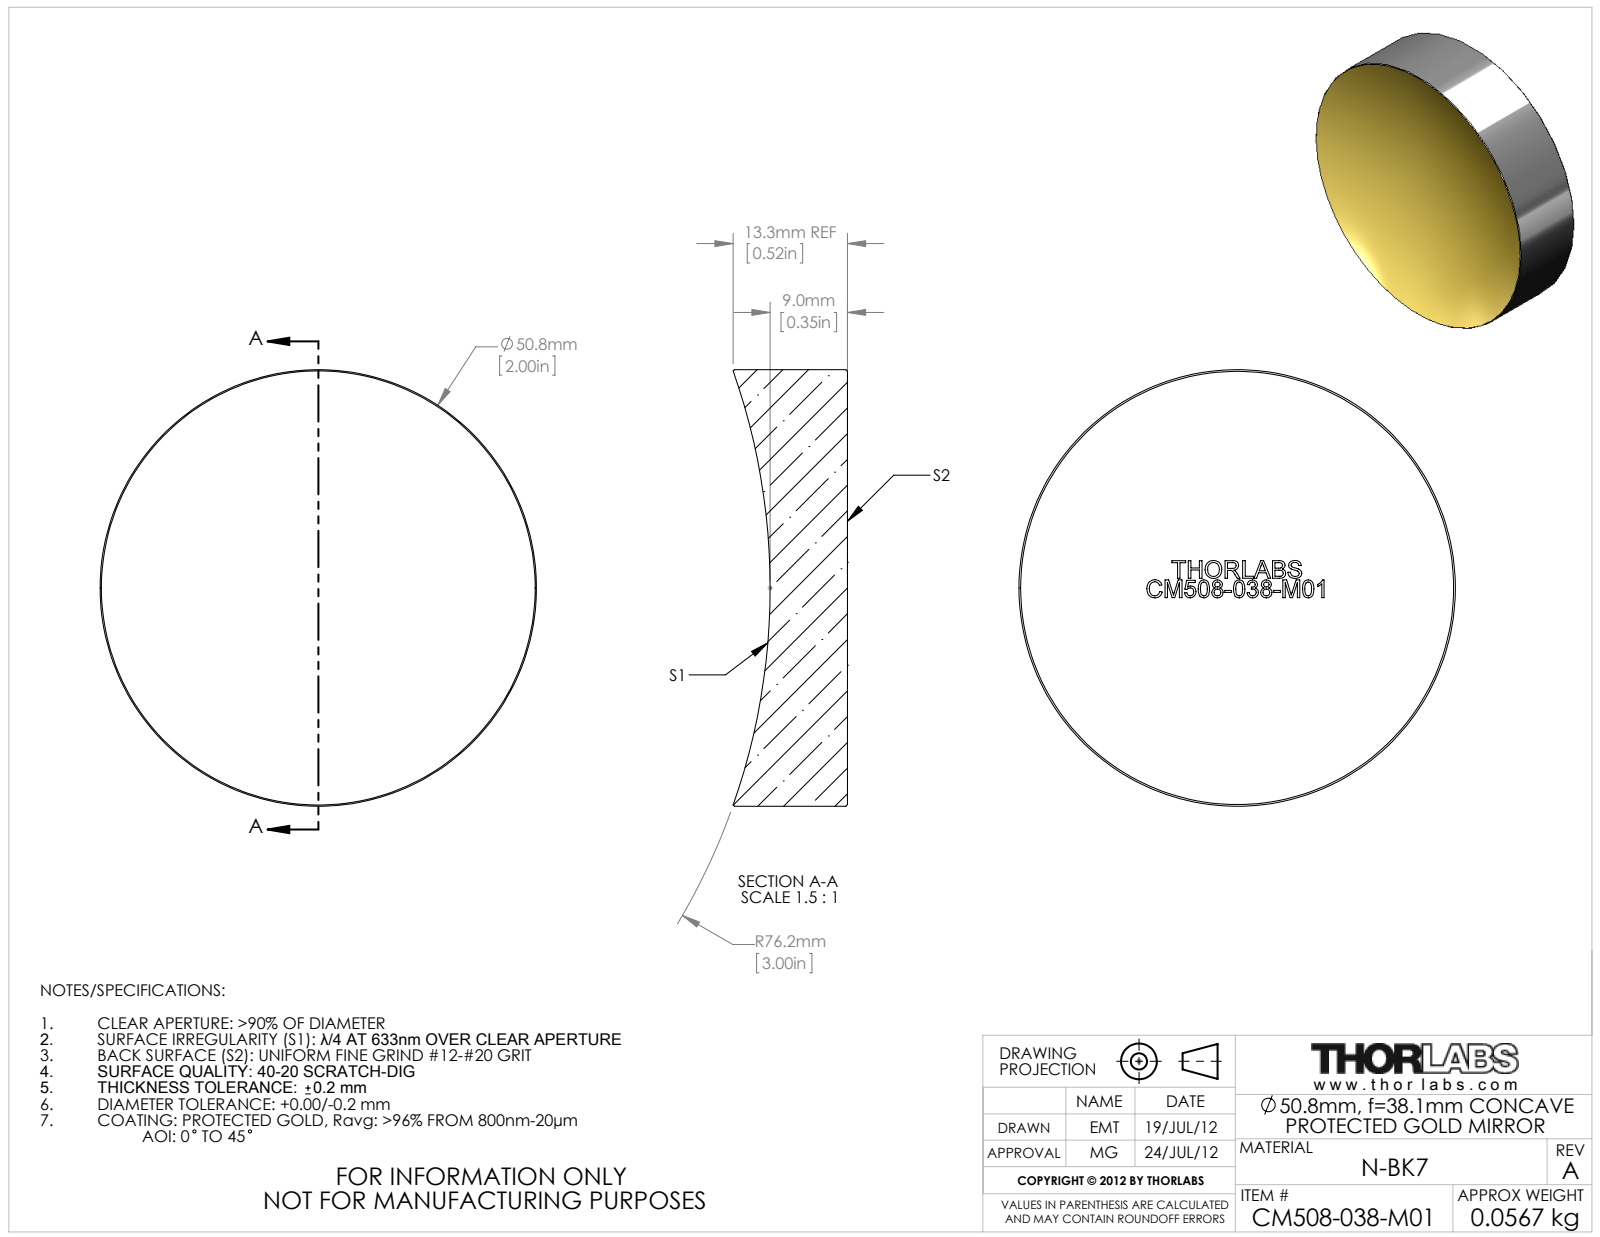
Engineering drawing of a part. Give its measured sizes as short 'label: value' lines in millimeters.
name: 24635-E0W
written by: SolidWorks 2011 (CONFIG_CONTROL_DESIGN)
unit: mm
bodies: 0 solids, 42 faces (34 planar, 2 cylindrical, 6 other)
size: 50.8 × 50.8 × 13.3
bosses: 1× ⌀50.8
